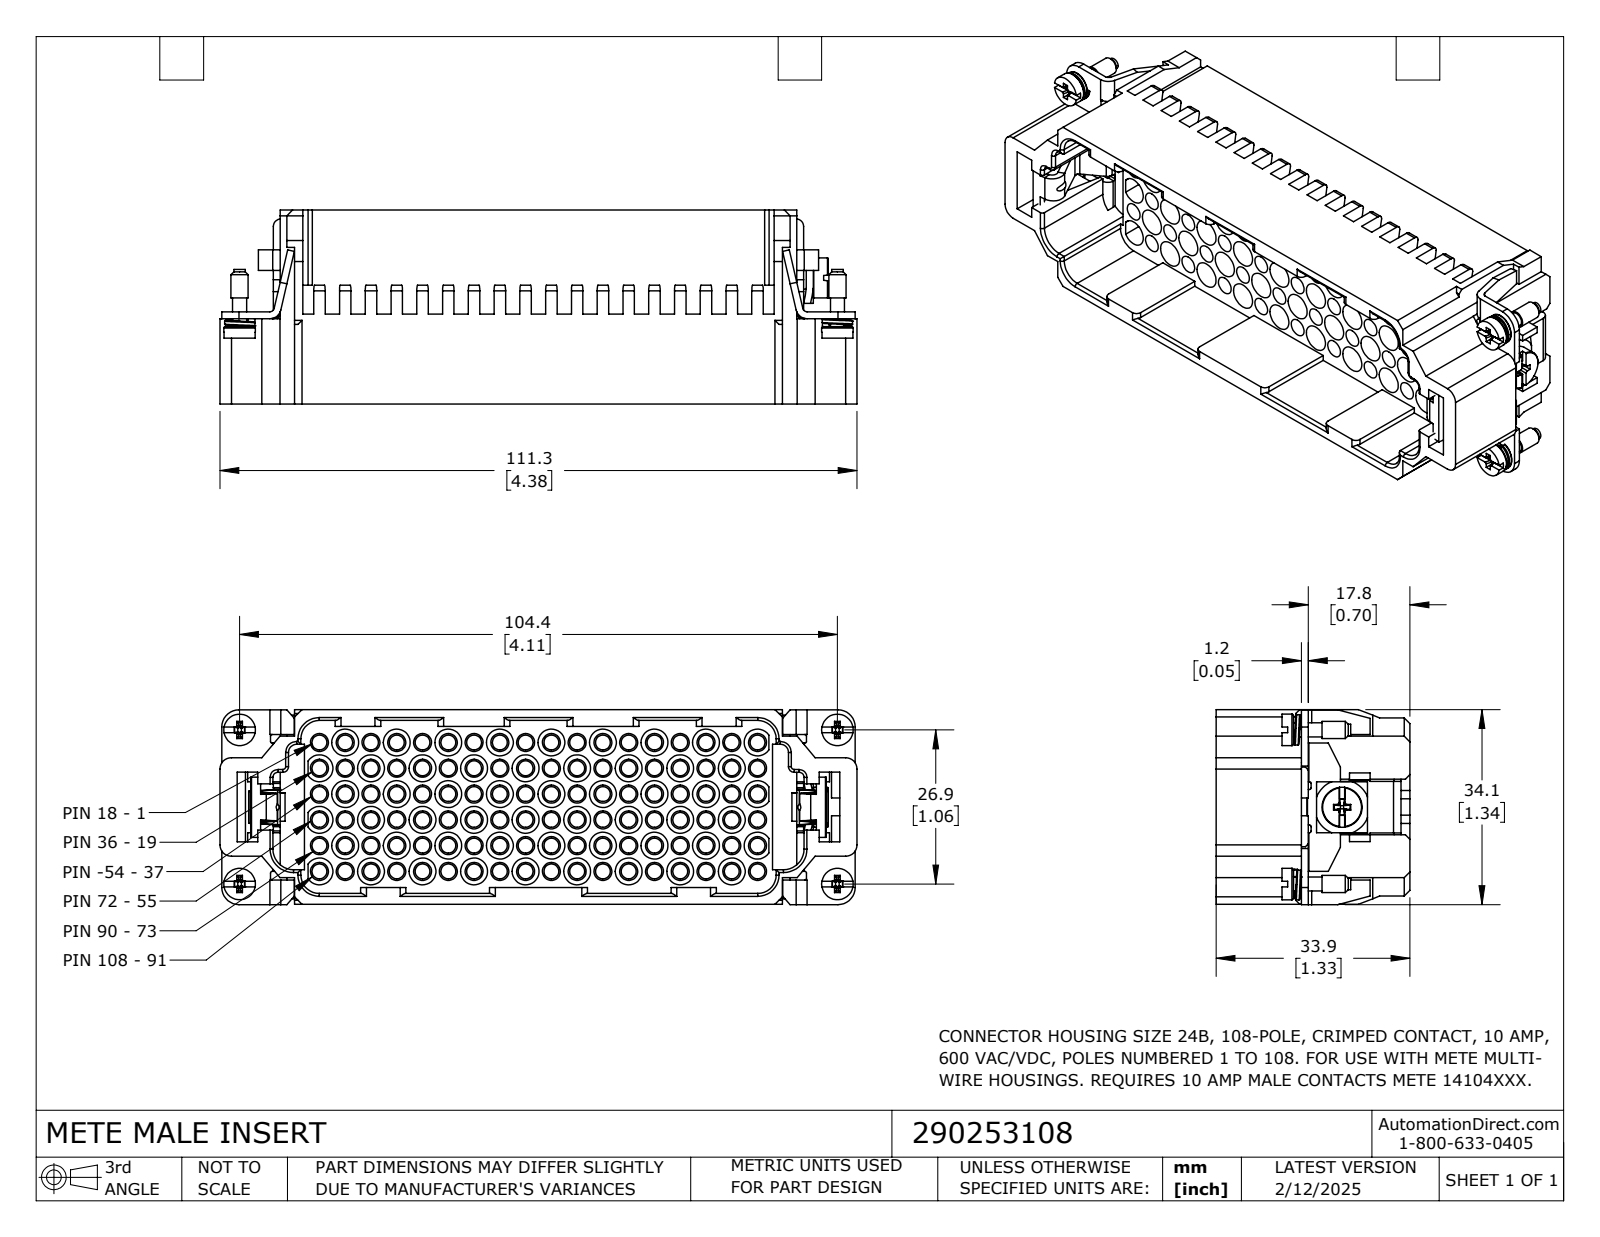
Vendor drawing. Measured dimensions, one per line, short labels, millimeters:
name: 290253108
written by: SolidWorks 2024 (CONFIG_CONTROL_DESIGN)
unit: mm
bodies: 13 solids, 2703 faces (1164 planar, 1456 cylindrical, 83 other)
size: 111.3 × 34.1 × 33.9
volume: 39 640 mm³; area: 48 850 mm²
holes: 108× ⌀2.6, 108× ⌀3.1, 108× ⌀3.5, 108× ⌀3.8, 54× ⌀4.7, 4× ⌀2.9, 1× ⌀3.3
bosses: 4× ⌀5.5, 4× ⌀5.3, 4× ⌀3, 4× ⌀2.4, 4× ⌀2, 1× ⌀7, 1× ⌀5, 1× ⌀3.9
rounds: 32× R0.3, 20× R1, 12× R0.3, 11× R0.5, 10× R0.1, 10× R1.3, 8× R1.3, 6× R2
face distances: 31.1, 2.9, 1.9, 34, 28.2, 1, 1.2, 3.7, 32.1, 29.2
hole spacings: 4.5, 9, 6.4, 13.5, 10.1, 14.2, 18, 18.5
